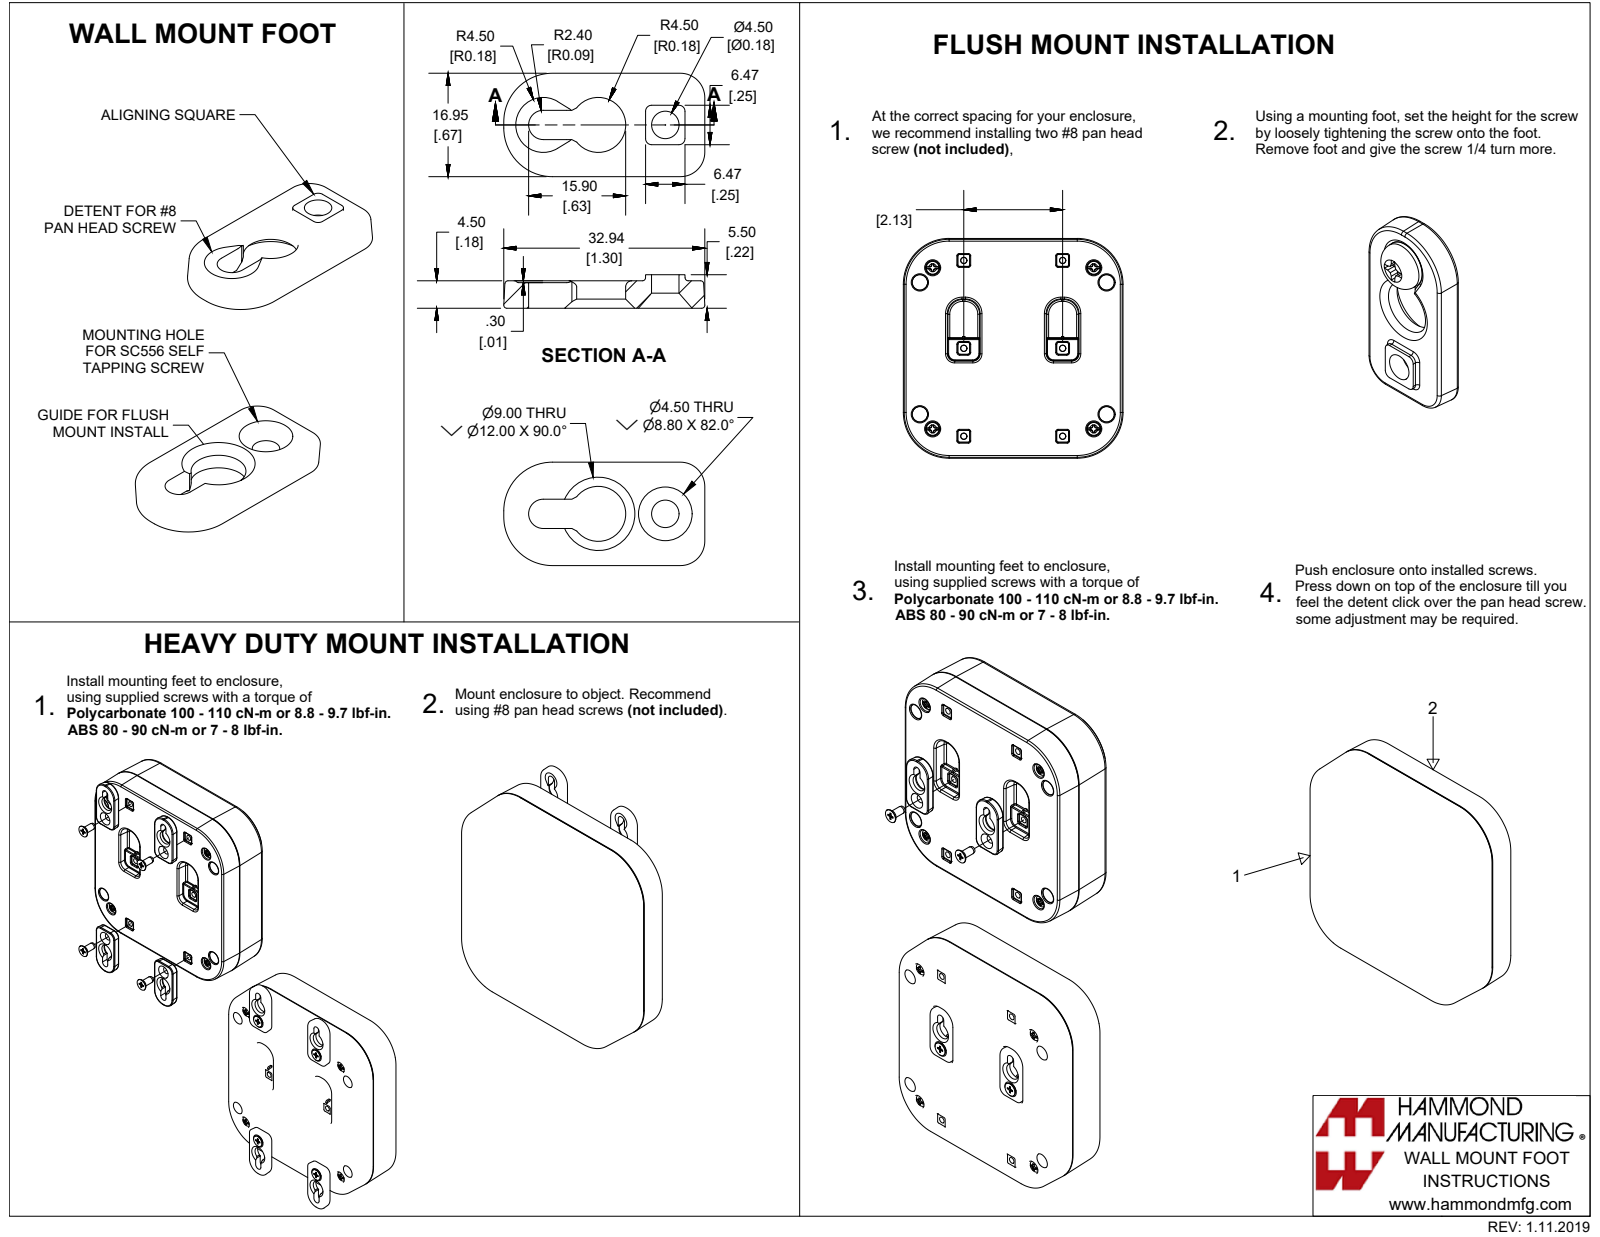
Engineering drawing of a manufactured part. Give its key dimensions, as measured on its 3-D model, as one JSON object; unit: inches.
{"part_name": "1557FOOT2GY-24", "step_written_by": "SolidWorks 2019 (CONFIG_CONTROL_DESIGN)", "units": "inches", "bodies": {"solids": 1, "faces": 57, "planar": 16, "cylindrical": 24, "other": 17}, "overall_size": [1.297, 0.667, 0.217], "volume_in3": 0.106, "surface_area_in2": 2.182, "round_holes": [[0.177, 1]], "partial_cylinders_radius": [[0.02, 14], [0.039, 4], [0.157, 2], [0.094, 1], [0.177, 1], [0.315, 1]], "face_to_face_distances": [0.177, 0.217, 0.039, 0.165, 0.051, 0.189]}
